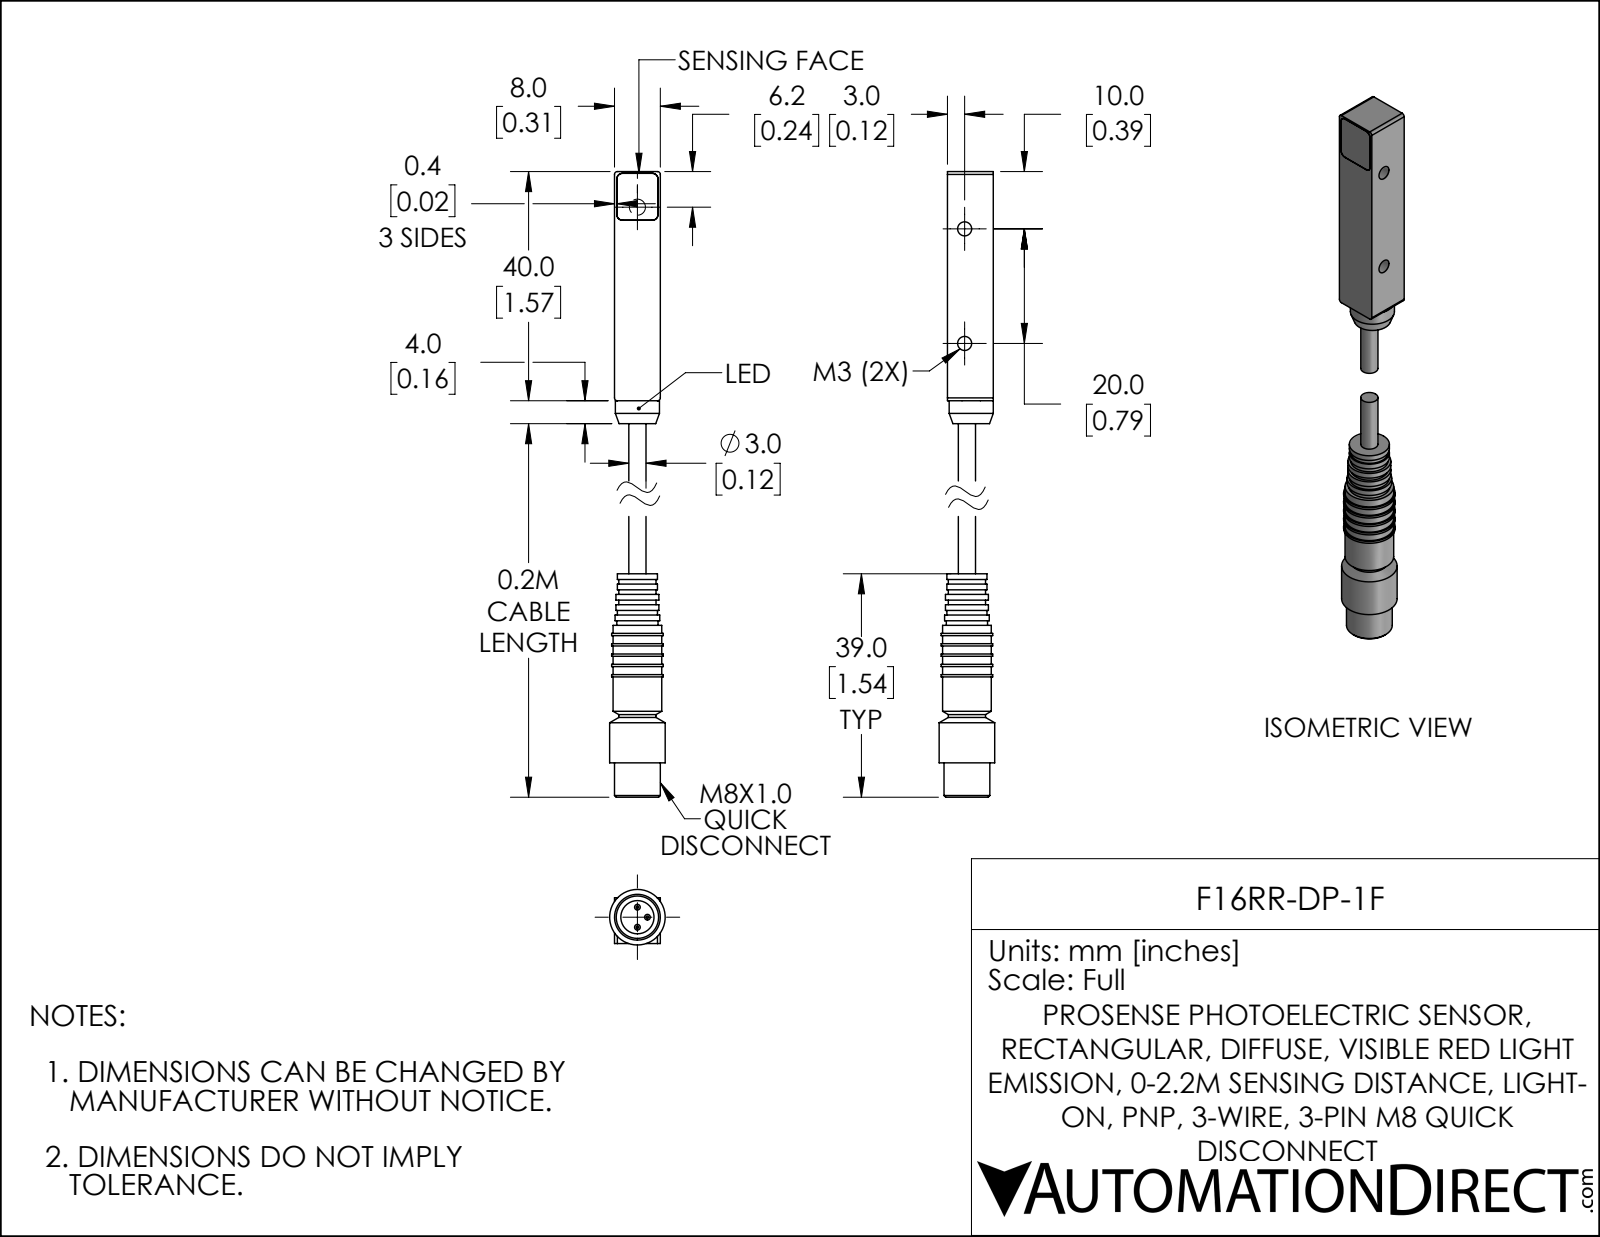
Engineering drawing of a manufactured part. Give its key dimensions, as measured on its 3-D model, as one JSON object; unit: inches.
{"part_name": "F16RR-DP-1F_2; F16RR-DP-1F; F16RR-DP-1F_1", "step_written_by": "SolidWorks 2019 (AUTOMOTIVE_DESIGN)", "units": "inches", "bodies": {"solids": 2, "faces": 102, "planar": 50, "cylindrical": 45, "other": 7}, "overall_size": [4.372, 0.382, 0.382], "volume_in3": 0.293, "surface_area_in2": 5.017, "round_holes": [[0.097, 2], [0.228, 1]], "round_bosses_or_shafts": [[0.039, 3], [0.382, 1], [0.354, 1], [0.335, 1], [0.315, 1], [0.307, 1], [0.303, 1], [0.295, 1]], "partial_cylinders_radius": [[0.02, 4], [0.039, 4], [0.039, 4]], "face_to_face_distances": [0.315, 0.142, 0.071, 0.213, 0.283, 0.354, 0.039, 1.732, 2.836, 2.443], "hole_center_spacings": [0.787]}
